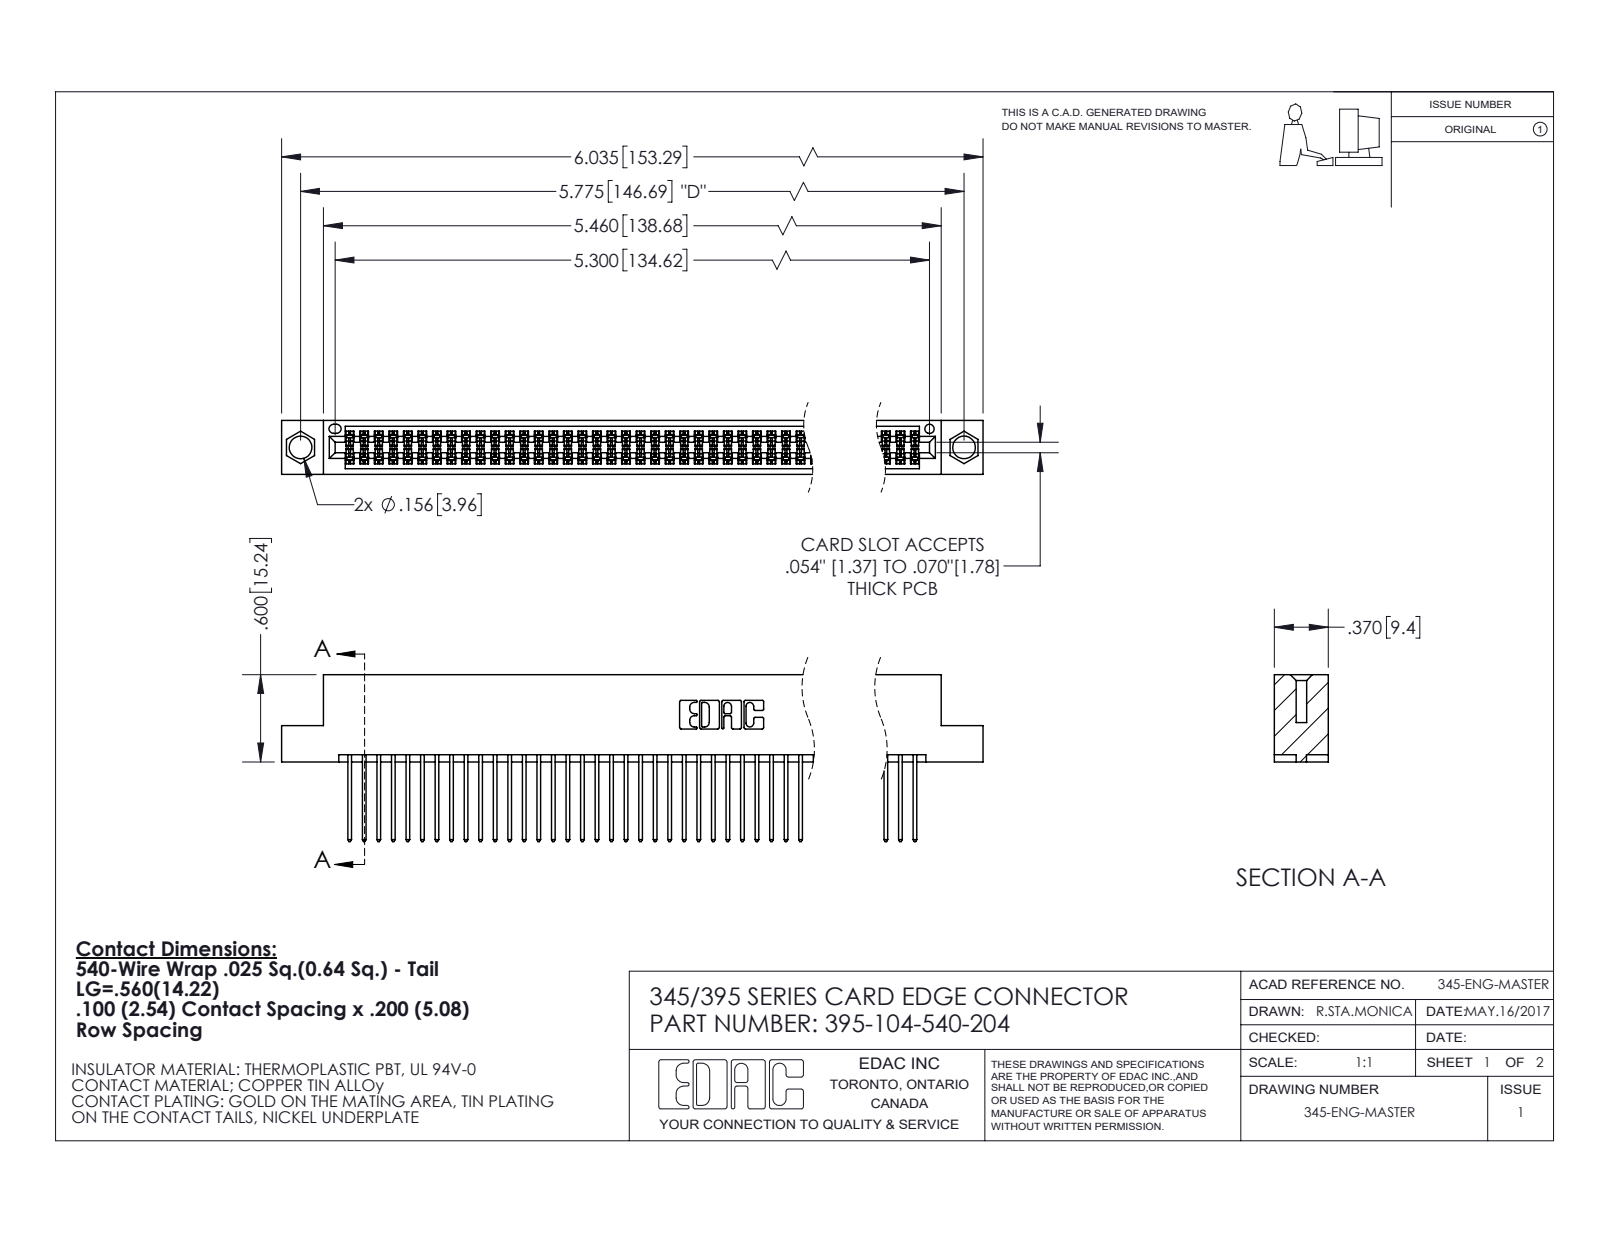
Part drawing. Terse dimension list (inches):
name: 345-292-001_345-293-140; 395-104-540-204; 345 Part_Flush Mounting Lugs - 0.156 Dia-TI
written by: SolidWorks 2020 (CONFIG_CONTROL_DESIGN)
unit: in
bodies: 105 solids, 5340 faces (3526 planar, 1814 cylindrical, 0 other)
size: 6.035 × 1.147 × 0.37
volume: 0.932 in³; area: 37.9 in²
holes: 2× ⌀0.156, 1× ⌀0.064
rounds: 156× R0.006, 104× R0.01, 22× R0.01, 6× R0.007, 6× R0.031, 3× R0.026, 2× R0.014, 2× R0.019
face distances: 0.298, 0.072, 0.2, 0.098, 0.272, 0.025, 0.37, 0.225, 0.175, 0.149
hole spacings: 0.27, 5.539, 5.775
